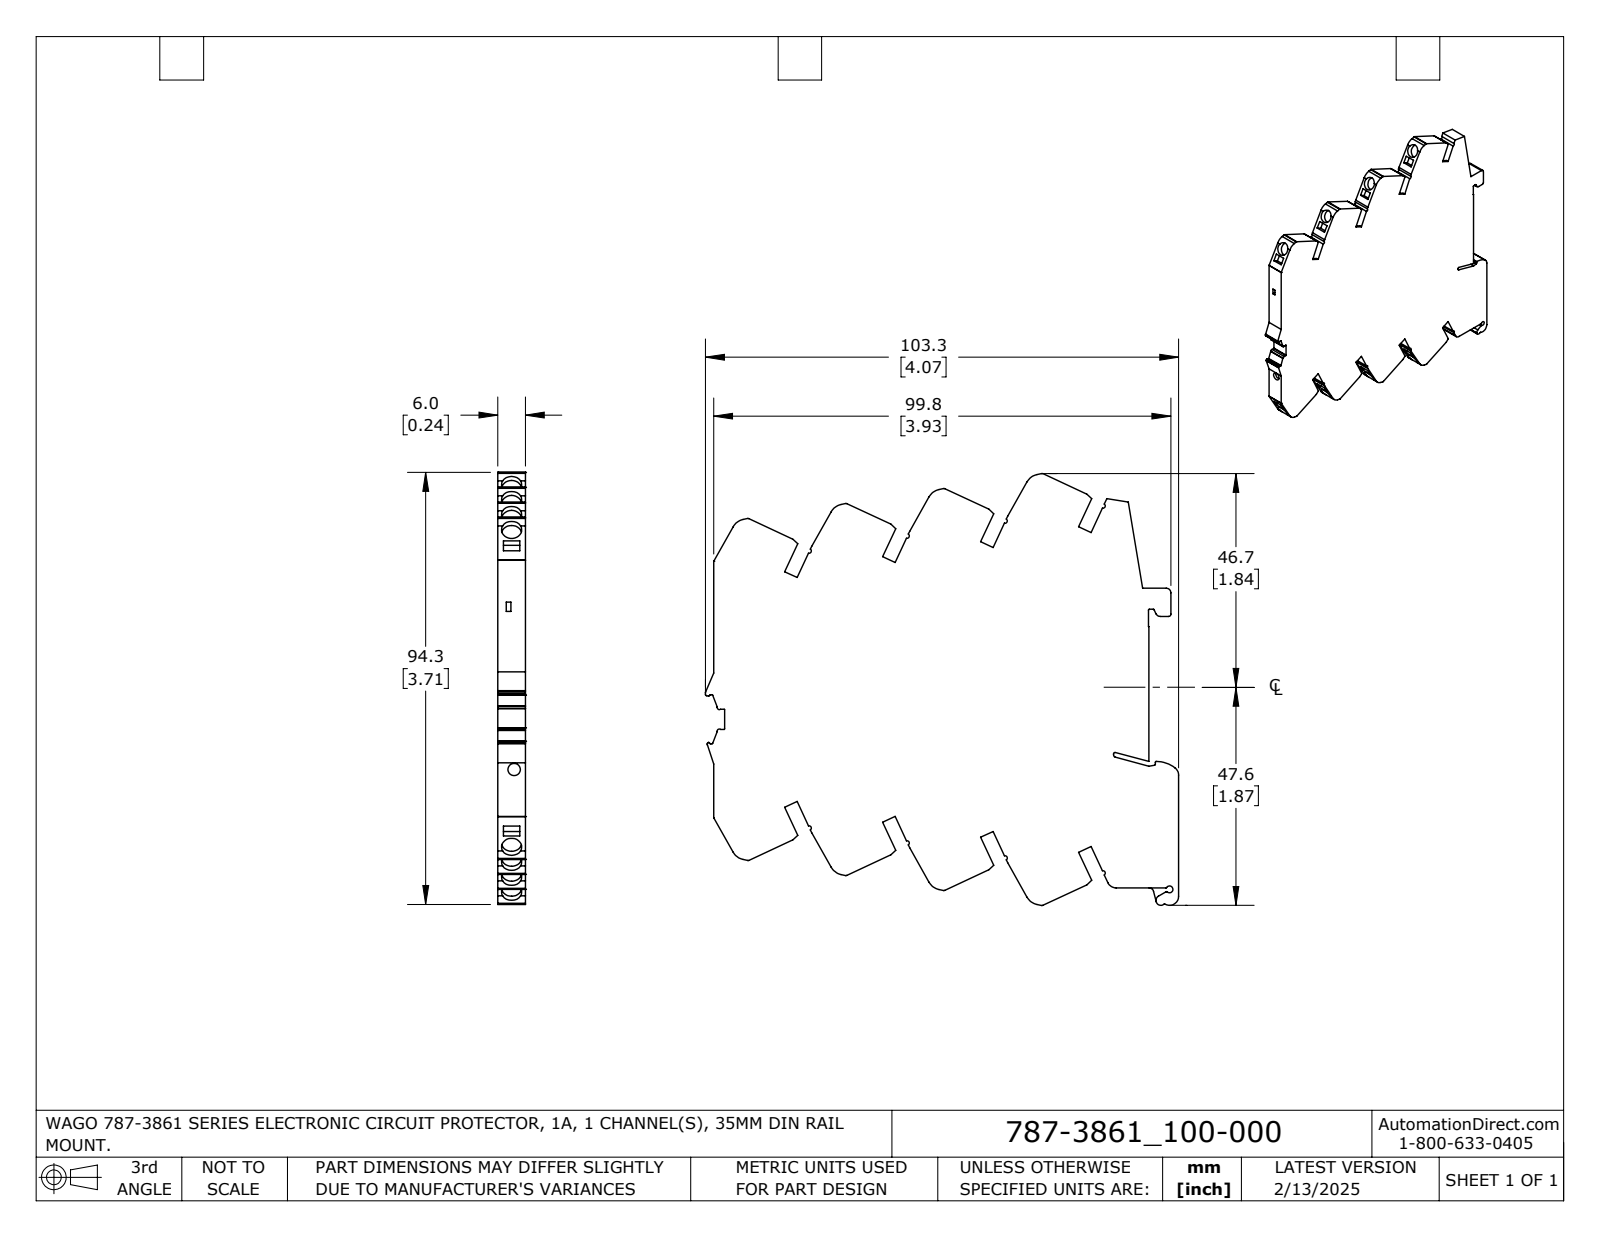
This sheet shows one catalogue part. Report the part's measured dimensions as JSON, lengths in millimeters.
{"part_name": "787-3861_100-000_HI", "step_written_by": "SolidWorks 2024 (AUTOMOTIVE_DESIGN)", "units": "millimeters", "bodies": {"solids": 1, "faces": 262, "planar": 197, "cylindrical": 65, "other": 0}, "overall_size": [103.3, 94.26, 6], "volume_mm3": 43992, "surface_area_mm2": 18864, "round_holes": [[4.4, 8], [2.7, 1]], "partial_cylinders_radius": [[0.2, 13], [0.5, 12], [0.4, 8], [3.35, 8], [1, 5], [0.3, 3], [2, 3], [0.45, 2]], "face_to_face_distances": [6, 17.99, 17.02, 3, 35.98, 12.01, 20.99, 14.99, 34.04, 12], "hole_center_spacings": [13.35, 26.7, 13.34, 40.05, 26.71]}
